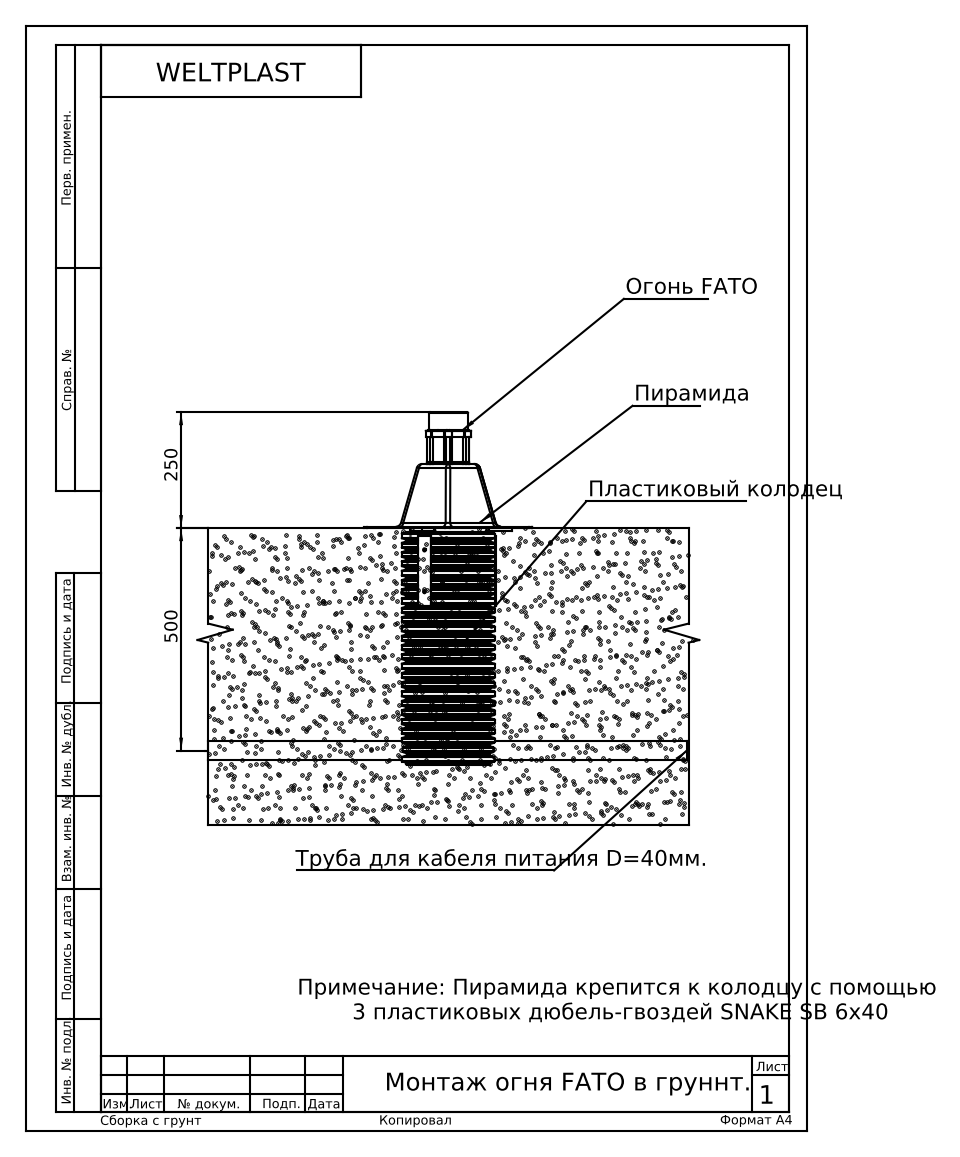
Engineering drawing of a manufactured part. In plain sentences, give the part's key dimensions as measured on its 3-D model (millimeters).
The part is named "Угол-1; LLC-AC-U1; LLC-AC-D2; Конектор мама Сборка 1 (+8 more)". Its 3-D file was written by "SolidWorks 2017 (AUTOMOTIVE_DESIGN)". It is 41 solids with 1955 faces: 626 planar, 805 cylindrical and 524 other. Overall it measures 1028.59 by 758.25 by 411.96 millimeters. Its volume is 4 225 000 cubic millimeters and its surface area 1 537 000 square millimeters. Round holes: 6 of diameter 4.4, 6 of diameter 4.5, 6 of diameter 6, 6 of diameter 6.5, 5 of diameter 5, 4 of diameter 5.3, 3 of diameter 4, 2 of diameter 4.2, 2 of diameter 12.6, 2 of diameter 20.25, 1 of diameter 26, 1 of diameter 40. Round bosses or shafts: 6 of diameter 7.6, 3 of diameter 5, 3 of diameter 4, 2 of diameter 21.5, 2 of diameter 19.7, 2 of diameter 15, 1 of diameter 200, 1 of diameter 180. Partial cylindrical surfaces (rounded edges, fillets, slot ends): 28 of radius 2, 26 of radius 12, 25 of radius 5, 18 of radius 4.5, 16 of radius 1, 14 of radius 1.5, 12 of radius 3, 9 of radius 7. The main face-to-face distances are 3, 1.5, 6, 2, 64.5, 13, 21, 15, 19, 135. The hole center spacings are 47.5, 82.27, 41.18, 48.09, 55.83, 42.28, 90, 95.
